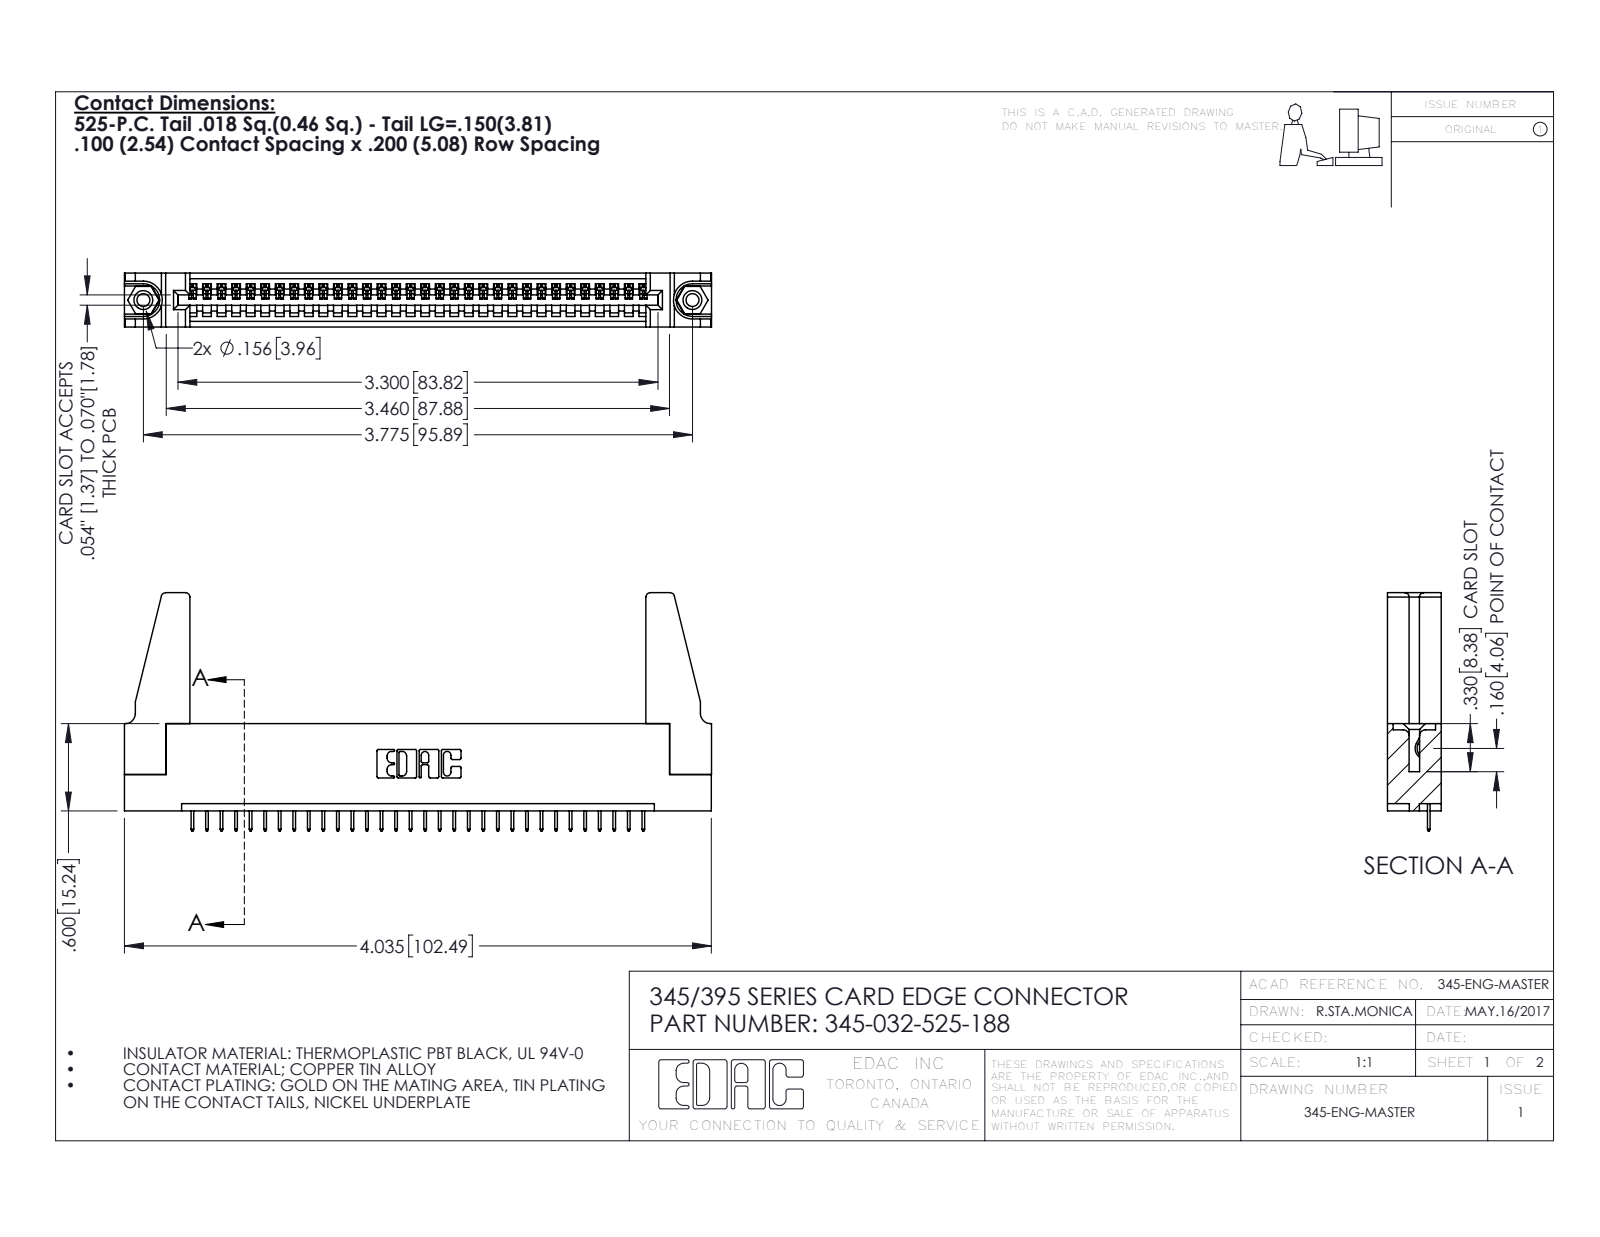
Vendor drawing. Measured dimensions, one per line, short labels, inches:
name: 345-250-001_345-250-001-102; 345-220-078_345-220-088; 345-292-001_345-293-125; 345-032-525-188 (+1 more)
written by: SolidWorks 2020 (CONFIG_CONTROL_DESIGN)
unit: in
bodies: 37 solids, 2234 faces (1624 planar, 594 cylindrical, 16 other)
size: 4.036 × 1.637 × 0.37
volume: 0.78 in³; area: 23.58 in²
holes: 2× ⌀0.089, 2× ⌀0.125, 2× ⌀0.156, 1× ⌀0.064
bosses: 2× ⌀0.155
rounds: 64× R0.006, 22× R0.01, 8× R0.03, 6× R0.007, 6× R0.031, 3× R0.026, 2× R0.031, 2× R0.04
face distances: 0.072, 0.37, 0.298, 0.2, 0.098, 0.272, 0.025, 0.225, 0.072, 0.149
hole spacings: 0.27, 3.54, 3.775
